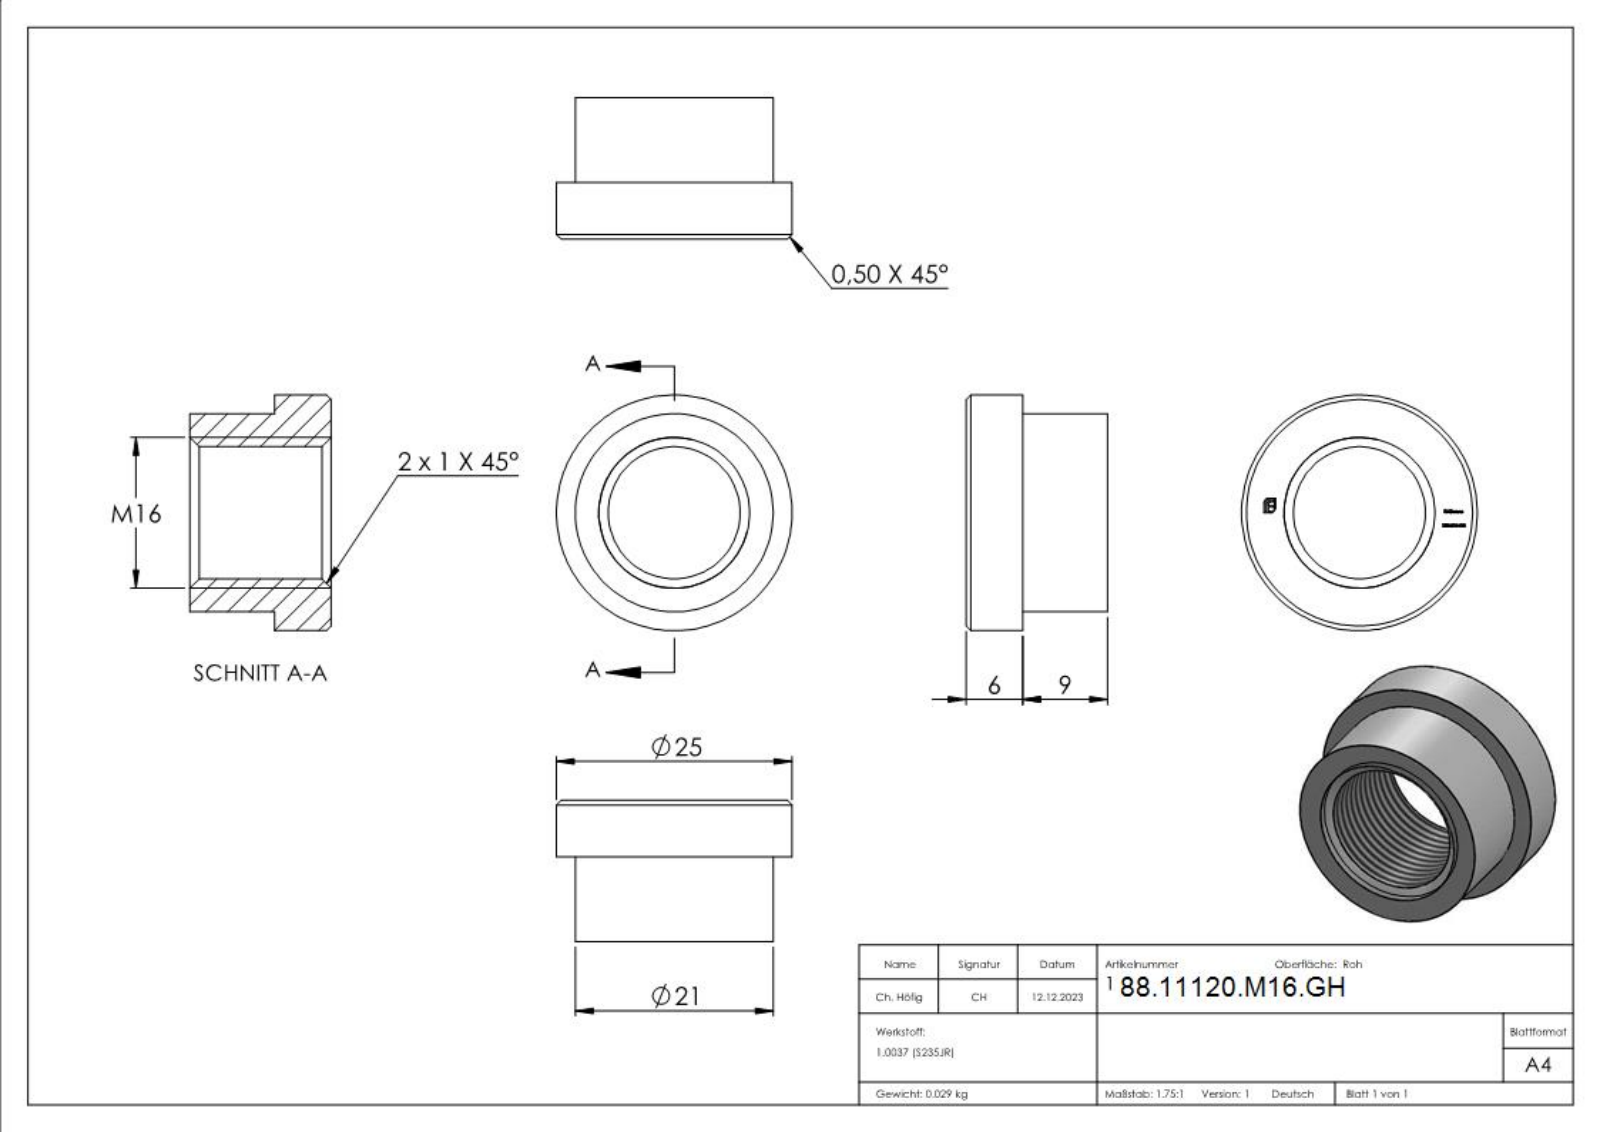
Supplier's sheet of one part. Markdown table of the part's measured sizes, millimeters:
| quantity | value |
| --- | --- |
| part name | 120-M16-GH |
| STEP written by | SolidWorks 2018 (CONFIG_CONTROL_DESIGN) |
| units | millimeters |
| bodies | 1 solid, 268 faces (161 planar, 3 cylindrical, 104 other) |
| overall size | 25 × 25 × 15 |
| volume | 3 698 mm³ |
| surface area | 2 330 mm² |
| round holes (diameter × count) | 14 × 1 |
| round bosses / shafts (diameter × count) | 25 × 1, 21 × 1 |
| main face-to-face distances | 15, 6, 9, 5.9, 14.9, 1.23, 1.5, 1.47, 0.47, 1.45 |
